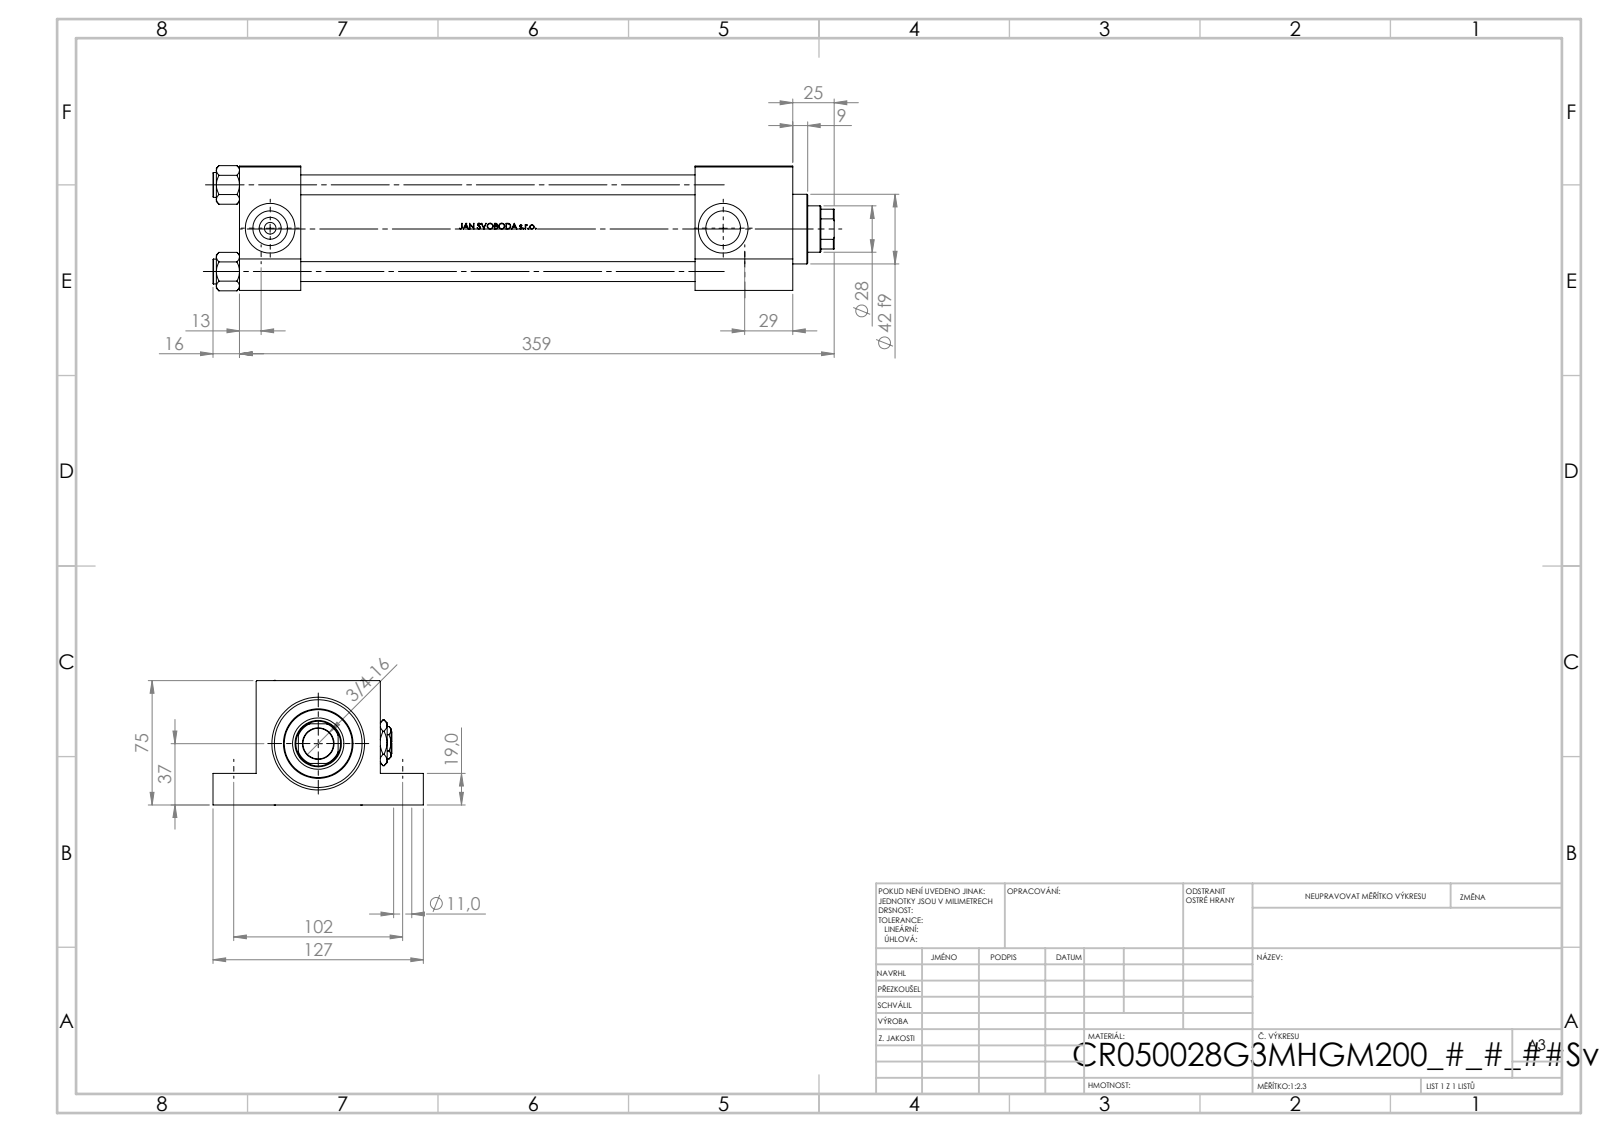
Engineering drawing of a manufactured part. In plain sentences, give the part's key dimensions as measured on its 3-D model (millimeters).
The part is named "V215_VC_A; Zatka_pro_OIL_PORT; NUT_M5_G; V215CR_G_Body (+2 more)". Its 3-D file was written by "SolidWorks 2019 (CONFIG_CONTROL_DESIGN)". It is 13 solids with 1183 faces: 477 planar, 132 cylindrical and 574 other. Overall it measures 375 by 127 by 75.54 millimeters. Its volume is 1 045 000 cubic millimeters and its surface area 270 482 square millimeters. Round holes: 4 of diameter 11, 4 of diameter 12, 2 of diameter 7, 2 of diameter 20.96, 2 of diameter 30, 1 of diameter 18.5, 1 of diameter 28, 1 of diameter 31, 1 of diameter 41, 1 of diameter 50, 1 of diameter 53. Round bosses or shafts: 4 of diameter 15, 1 of diameter 56, 1 of diameter 42. Partial cylindrical surfaces (rounded edges, fillets, slot ends): 1 of radius 13.5. The main face-to-face distances are 75, 37, 334, 297, 19, 56, 275, 238, 59, 26. The hole center spacings are 52.3, 36.63, 37.34, 73.96, 102, 292, 309.3, 273.5.
